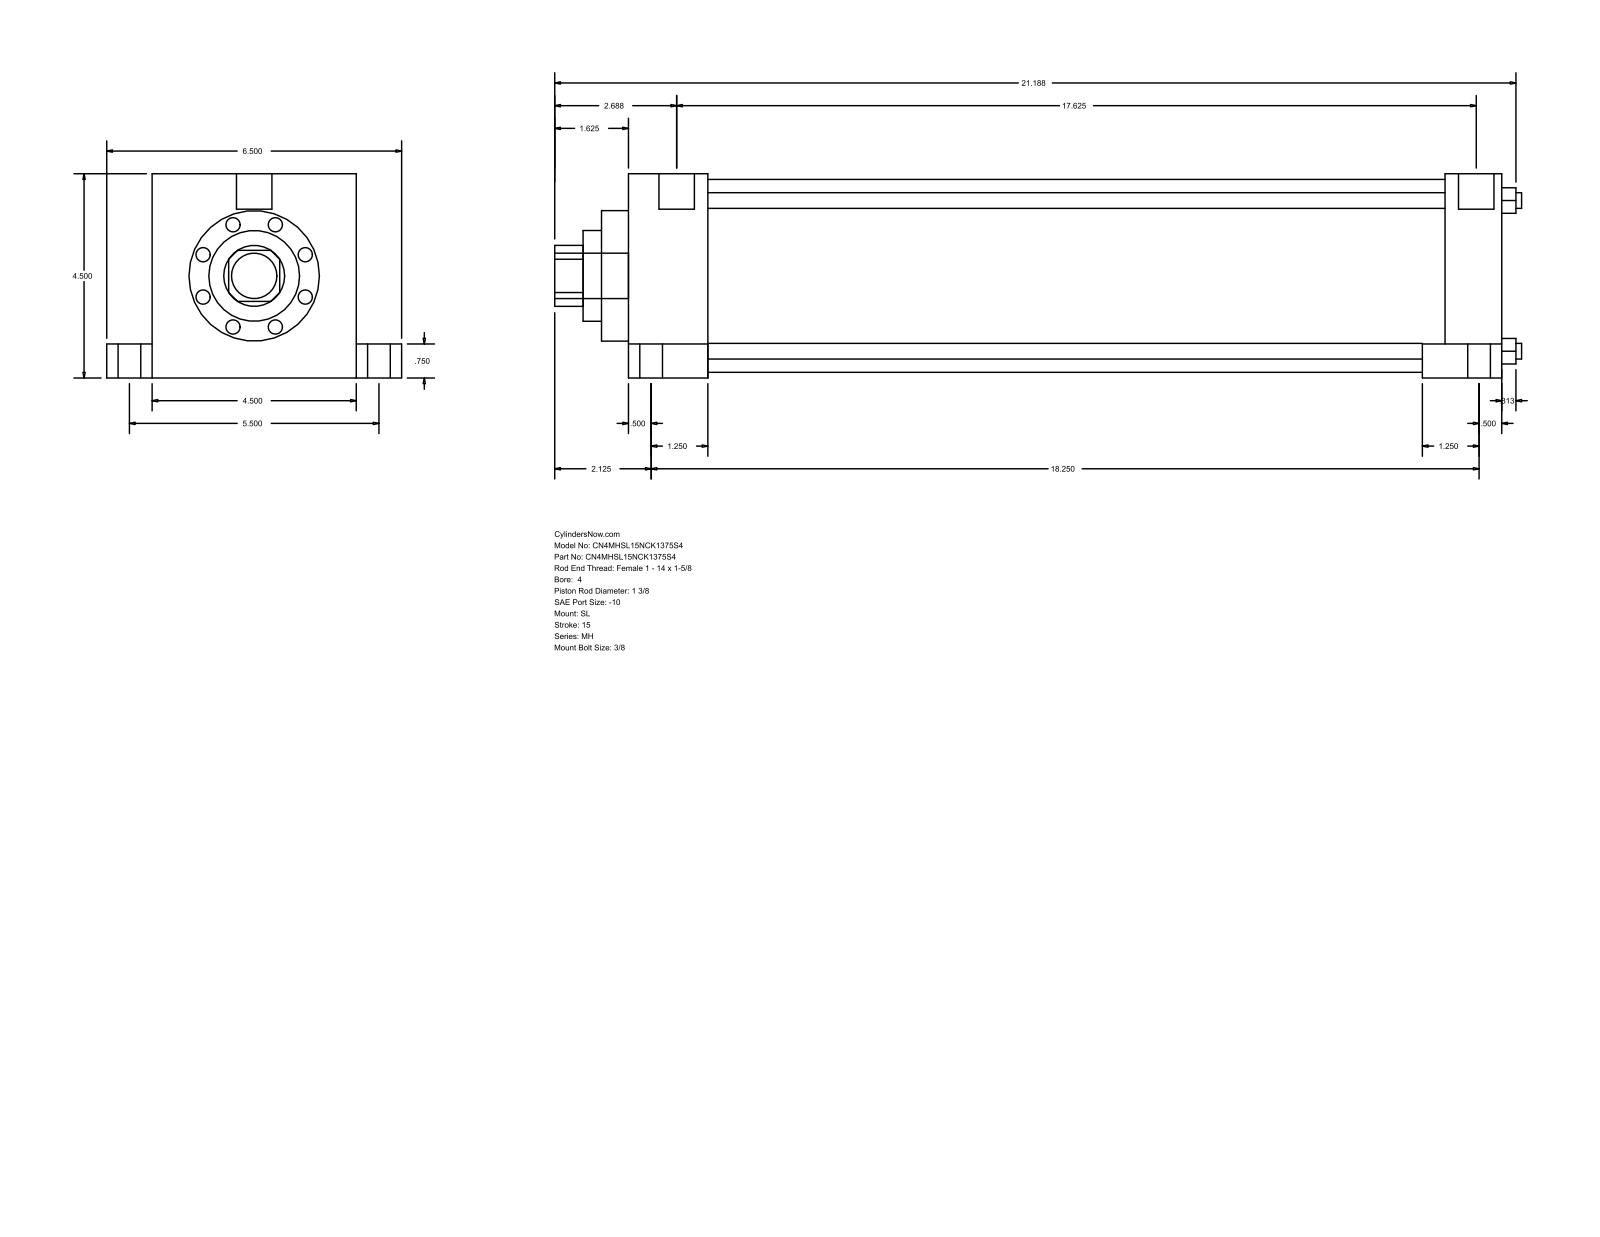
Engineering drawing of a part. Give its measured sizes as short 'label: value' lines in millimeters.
name: MH_SL__0400_1.375
written by: GSSL Pune (CONFIG_CONTROL_DESIGN)
unit: mm
bodies: 0 solids, 110 faces (77 planar, 33 cylindrical, 0 other)
size: 541.34 × 165.1 × 114.3
holes: 4× ⌀8.76, 1× ⌀34.92, 1× ⌀50.8, 1× ⌀73.03, 1× ⌀107.95
bosses: 4× ⌀19.05, 4× ⌀12.7, 4× ⌀8.73, 2× ⌀19.84, 1× ⌀25.4
rounds: 1× R17.06
face distances: 114.3, 488.96, 44.45, 444.51, 457.21, 412.76, 31.75, 25.4, 139.7, 19.05
hole spacings: 59.62, 84.32, 119.25
